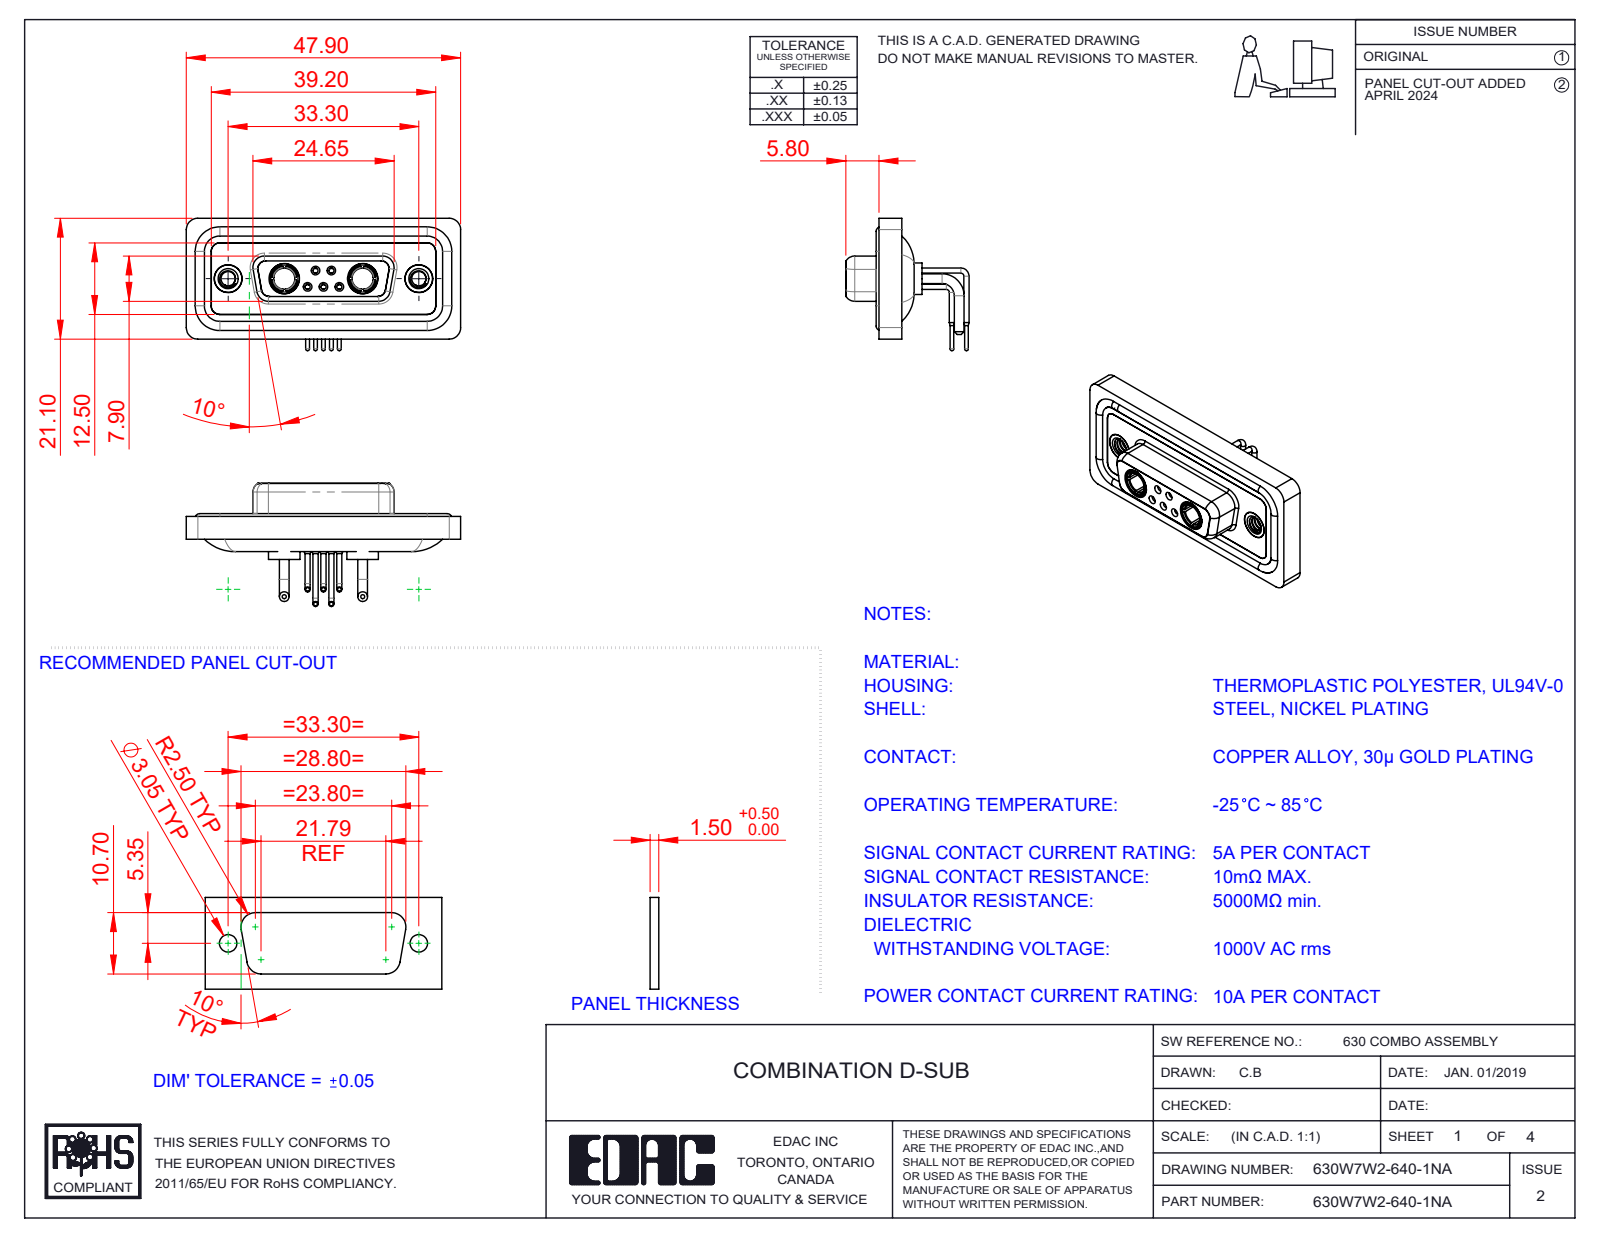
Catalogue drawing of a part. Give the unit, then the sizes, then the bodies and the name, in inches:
Units: inches
Overall size (bounding box): 1.886 × 0.91 × 0.848
Round holes (diameter × count): ⌀0.035 ×5, ⌀0.043 ×5, ⌀0.059 ×5, ⌀0.079 ×5, ⌀0.191 ×4, ⌀0.063 ×3, ⌀0.067 ×2, ⌀0.098 ×2, ⌀0.146 ×2, ⌀0.157 ×2, ⌀0.159 ×2, ⌀0.197 ×2
Round bosses / shafts (diameter × count): ⌀0.063 ×6, ⌀0.035 ×5, ⌀0.026 ×5, ⌀0.067 ×4, ⌀0.217 ×2, ⌀0.205 ×2, ⌀0.195 ×2, ⌀0.195 ×2
Partial cylindrical surfaces — rounded edges, fillets, slot ends (radius × count): R0.079 ×20, R0.059 ×18, R0.053 ×12, R0.063 ×8, R0.01 ×4, R0.02 ×4, R0.024 ×4, R0.026 ×4
Main face-to-face distances: 0.016, 0.071, 0.043, 0.063, 0.114, 0.098, 0.122, 0.146, 0.161, 0.059
Hole centre spacings: 0.124, 0.109, 0.386, 0.925, 0.17, 0.17, 0.198, 0.198
Volume: 0.371 in³ · Surface area: 15.67 in²
Bodies: 16 solids, 801 faces (238 planar, 351 cylindrical, 212 other)
Part name (STEP PRODUCT): 630W7W2-640-1NA; 630Combo Waterproof Housing_15 Contacts; 630Combo Shell Rear_15 Contacts; 630Combo Shell Front_15 Contacts (+5 more)
STEP written by: SolidWorks 2023 (CONFIG_CONTROL_DESIGN)
